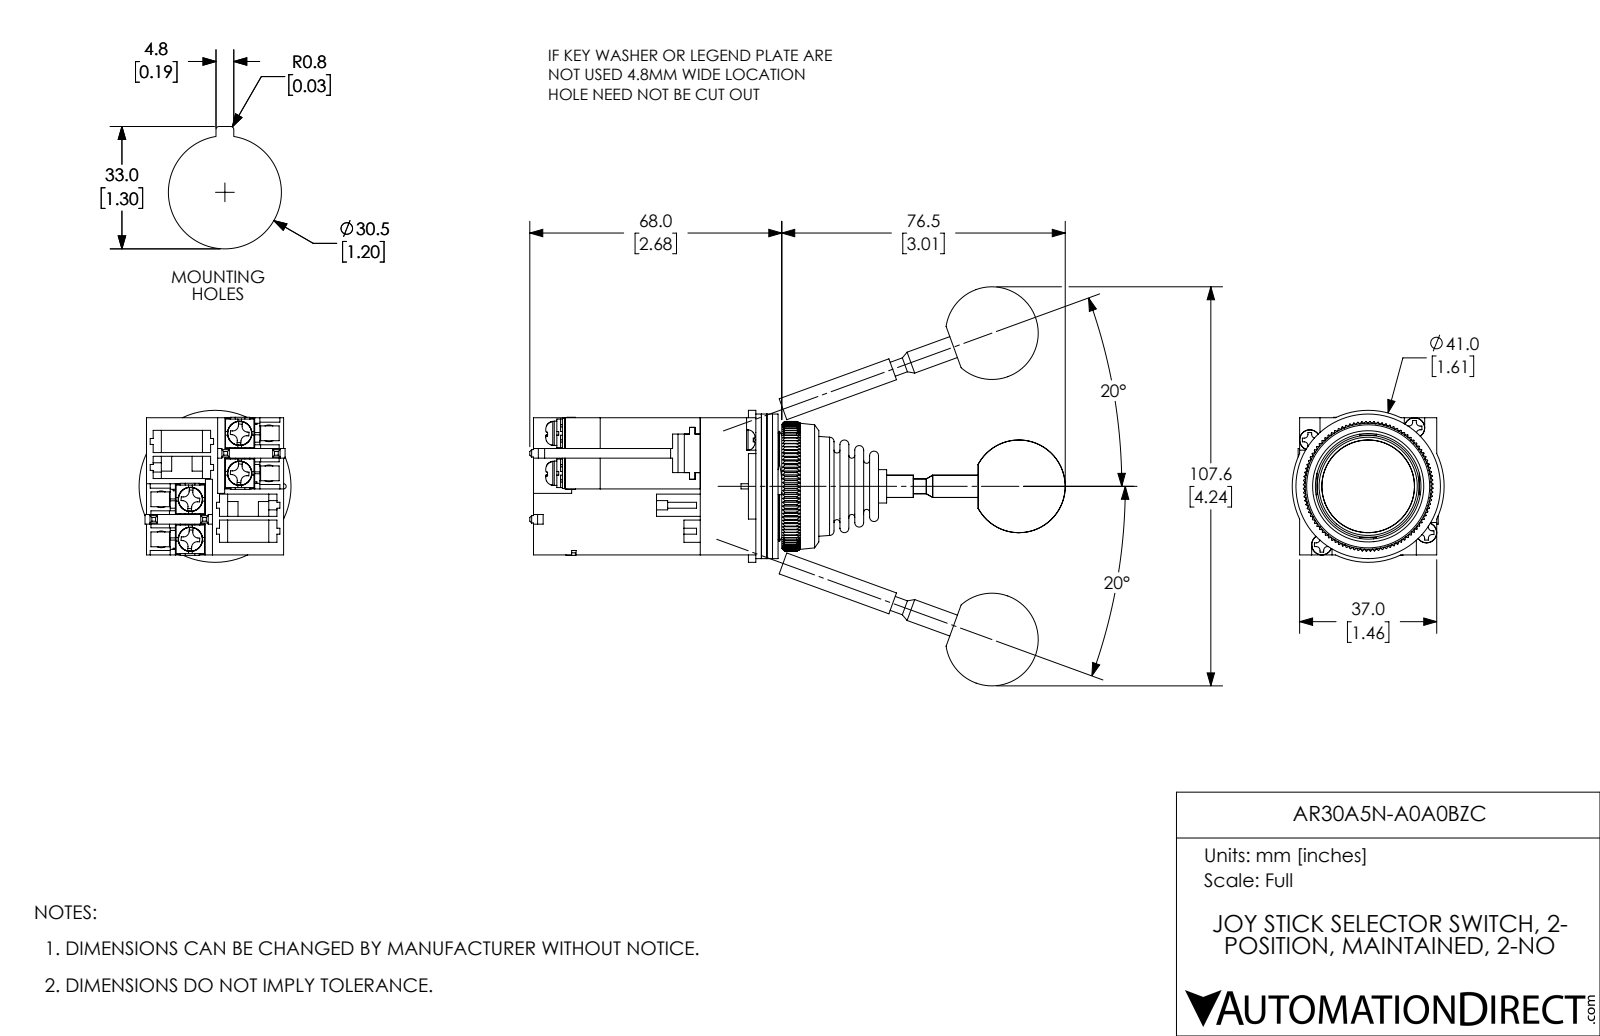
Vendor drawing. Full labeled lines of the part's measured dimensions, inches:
Part name (STEP PRODUCT): AR30A5N-A0A0BZC
STEP written by: SolidWorks 2017 (AUTOMOTIVE_DESIGN)
Units: inches
Bodies: 32 solids, 1971 faces (1388 planar, 321 cylindrical, 262 other)
Overall size (bounding box): 5.689 × 1.614 × 1.614
Volume: 4.184 in³ · Surface area: 68.68 in²
Round holes (diameter × count): ⌀0.118 ×8, ⌀0.138 ×4, ⌀0.142 ×4, ⌀0.315 ×1, ⌀0.874 ×1, ⌀1.122 ×1, ⌀1.173 ×1
Round bosses / shafts (diameter × count): ⌀0.26 ×4, ⌀1.535 ×1, ⌀1.181 ×1, ⌀0.984 ×1, ⌀0.354 ×1, ⌀0.236 ×1, ⌀0.157 ×1
Partial cylindrical surfaces — rounded edges, fillets, slot ends (radius × count): R0.039 ×16, R0.059 ×16, R0.029 ×8, R0.057 ×8, R0.089 ×8, R0.108 ×4, R0.028 ×1, R0.398 ×1
Main face-to-face distances: 0.059, 0.701, 0.756, 0.055, 0.118, 1.457, 0.177, 0.236, 0.449, 0.114
Hole centre spacings: 0.792, 1.12, 0.296, 0.365, 0.424, 0.756, 0.875, 1.583
